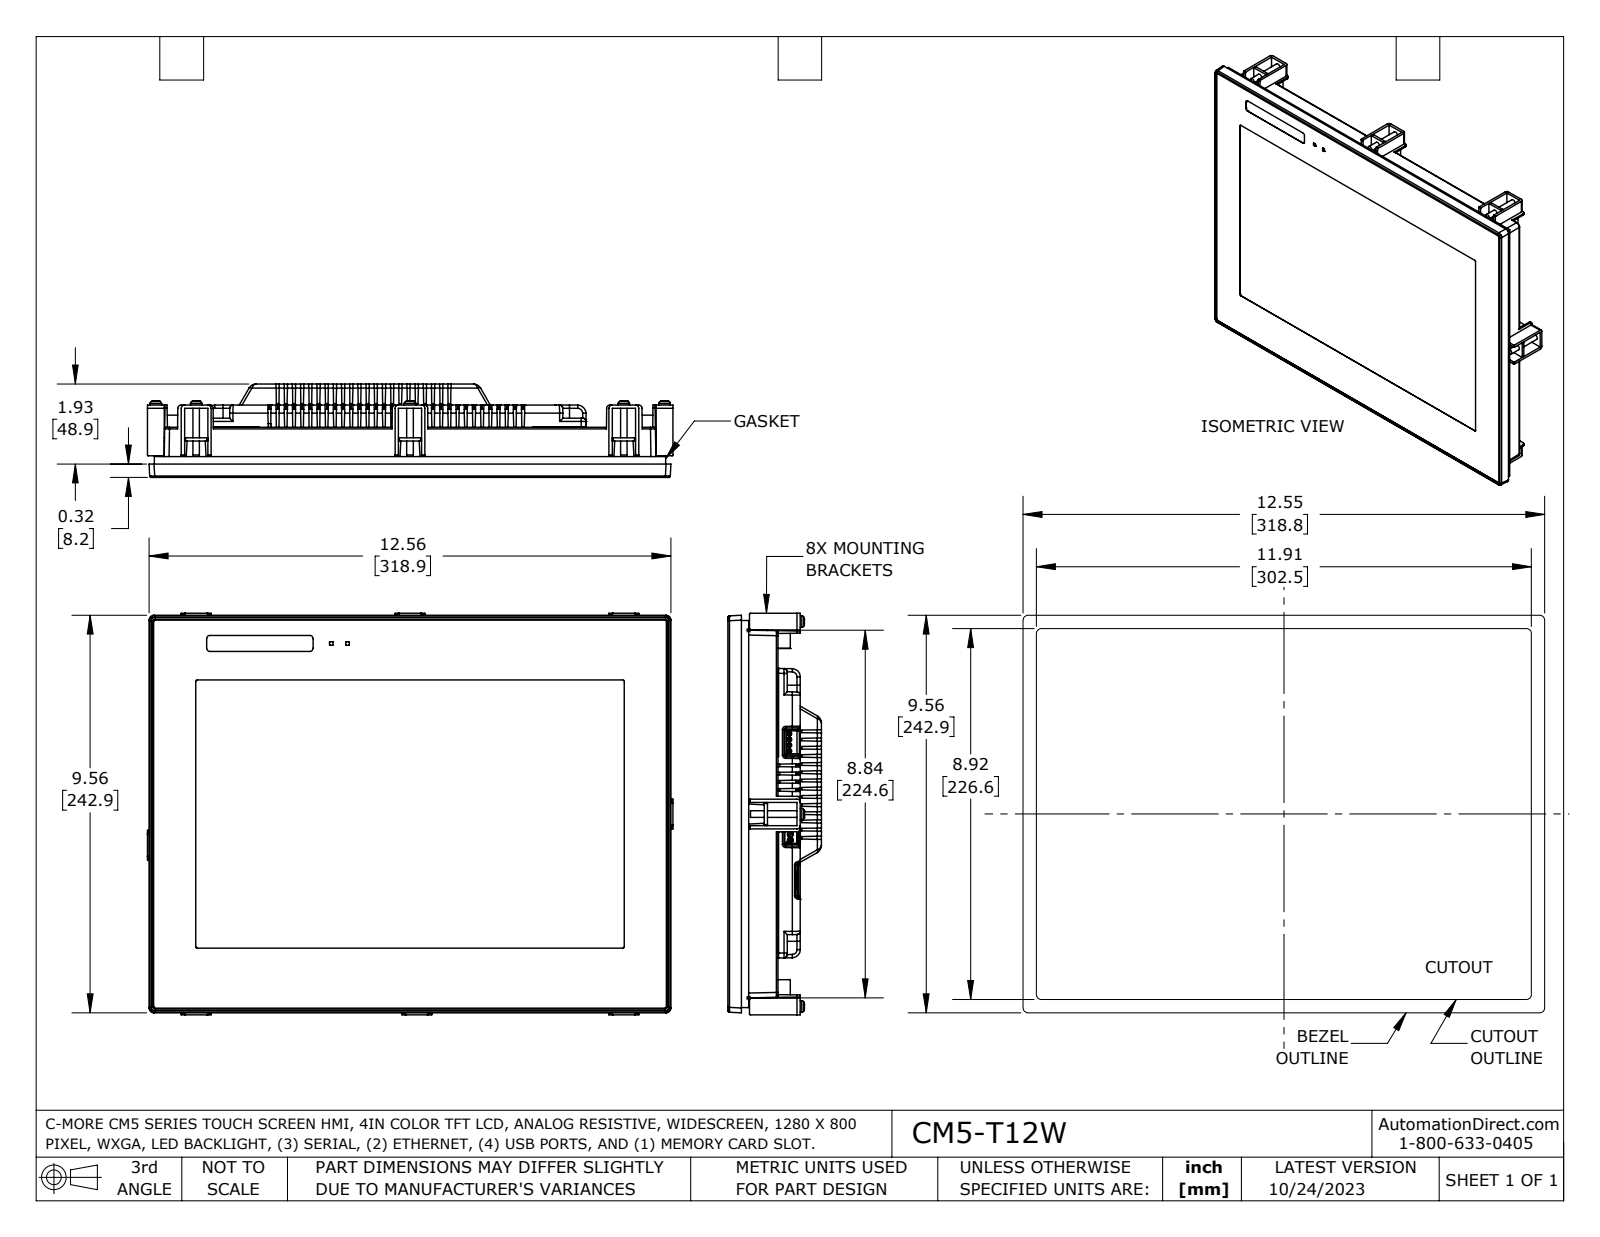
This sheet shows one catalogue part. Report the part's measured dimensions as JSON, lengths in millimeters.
{"part_name": "CM5-T12W", "step_written_by": "SolidWorks 2021 (AUTOMOTIVE_DESIGN)", "units": "millimeters", "bodies": {"solids": 1, "faces": 4659, "planar": 3145, "cylindrical": 1232, "other": 282}, "overall_size": [321.1, 245.3, 57.1], "volume_mm3": 2332000, "surface_area_mm2": 330100, "round_holes": [[0.9, 10], [2.8, 4], [2.9, 3], [2.5, 2]], "round_bosses_or_shafts": [[0.5, 12], [7, 8], [4, 8], [5.5, 4], [2.6, 4], [2.8, 3], [0.5, 1]], "partial_cylinders_radius": [[1, 119], [0.5, 117], [0.3, 90], [2, 85], [0.2, 72], [0.2, 52], [0.3, 33], [0.6, 29]], "face_to_face_distances": [43.9, 43.9, 36, 7.9, 8, 27.4, 8.6, 16.5, 16.5, 12.9], "hole_center_spacings": [3.1, 2.8, 3.5, 5.5, 5, 8.3, 5, 7]}
